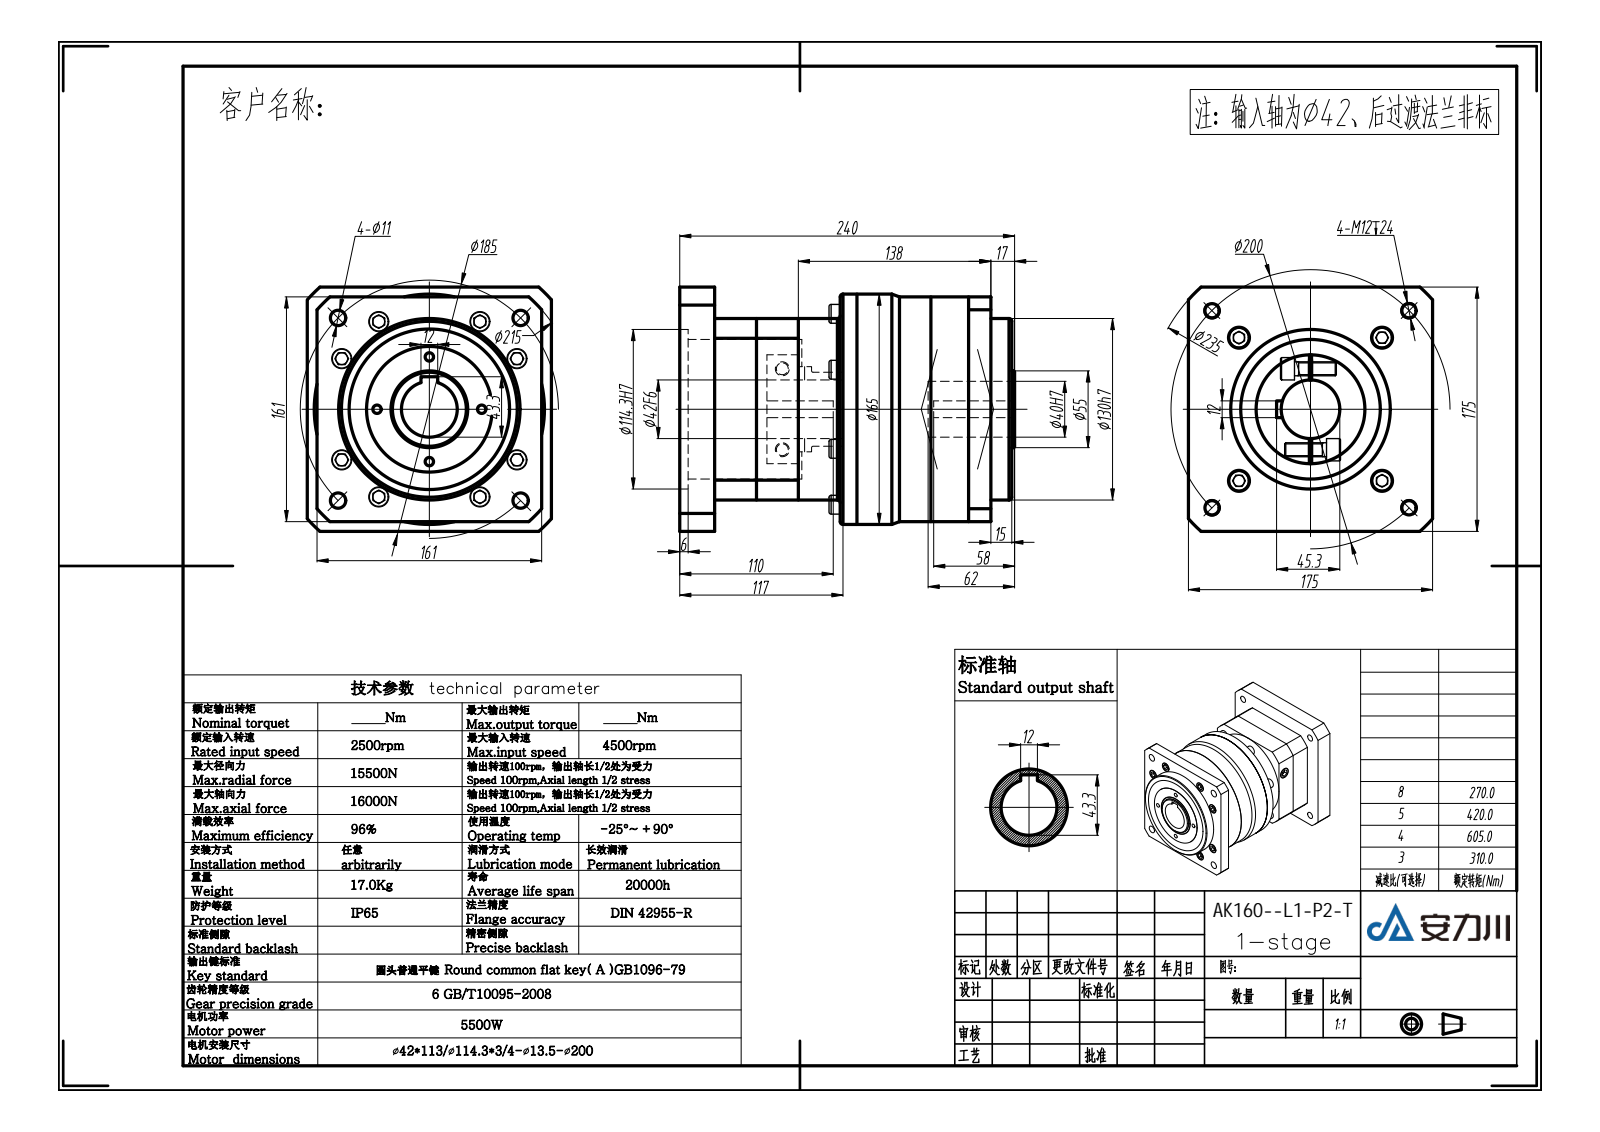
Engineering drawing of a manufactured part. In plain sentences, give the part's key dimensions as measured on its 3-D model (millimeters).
The part is named "VGK160单级模型-T（42-113 114.3-4 4-13.5-200）". Its 3-D file was written by "SolidWorks 2016 (AUTOMOTIVE_DESIGN)". It is 5 solids with 469 faces: 274 planar, 173 cylindrical and 22 other. Overall it measures 240 by 175 by 175 millimeters. Its volume is 3 886 000 cubic millimeters and its surface area 407 188 square millimeters. Round holes: 8 of diameter 14, 4 of diameter 6, 4 of diameter 6.8, 4 of diameter 10.2, 4 of diameter 11, 4 of diameter 15, 2 of diameter 16, 1 of diameter 40, 1 of diameter 42, 1 of diameter 61, 1 of diameter 90, 1 of diameter 100. Round bosses or shafts: 12 of diameter 13.5, 8 of diameter 13, 2 of diameter 15.6, 1 of diameter 165, 1 of diameter 161, 1 of diameter 130, 1 of diameter 78, 1 of diameter 60. Partial cylindrical surfaces (rounded edges, fillets, slot ends): 1 of radius 107.5, 1 of radius 115. The main face-to-face distances are 53, 155, 102, 30, 25, 180, 168, 127, 55, 22.5. The hole center spacings are 72.5, 18.93, 29.28, 35.36, 44.2, 53.09, 62.8, 71.12.
